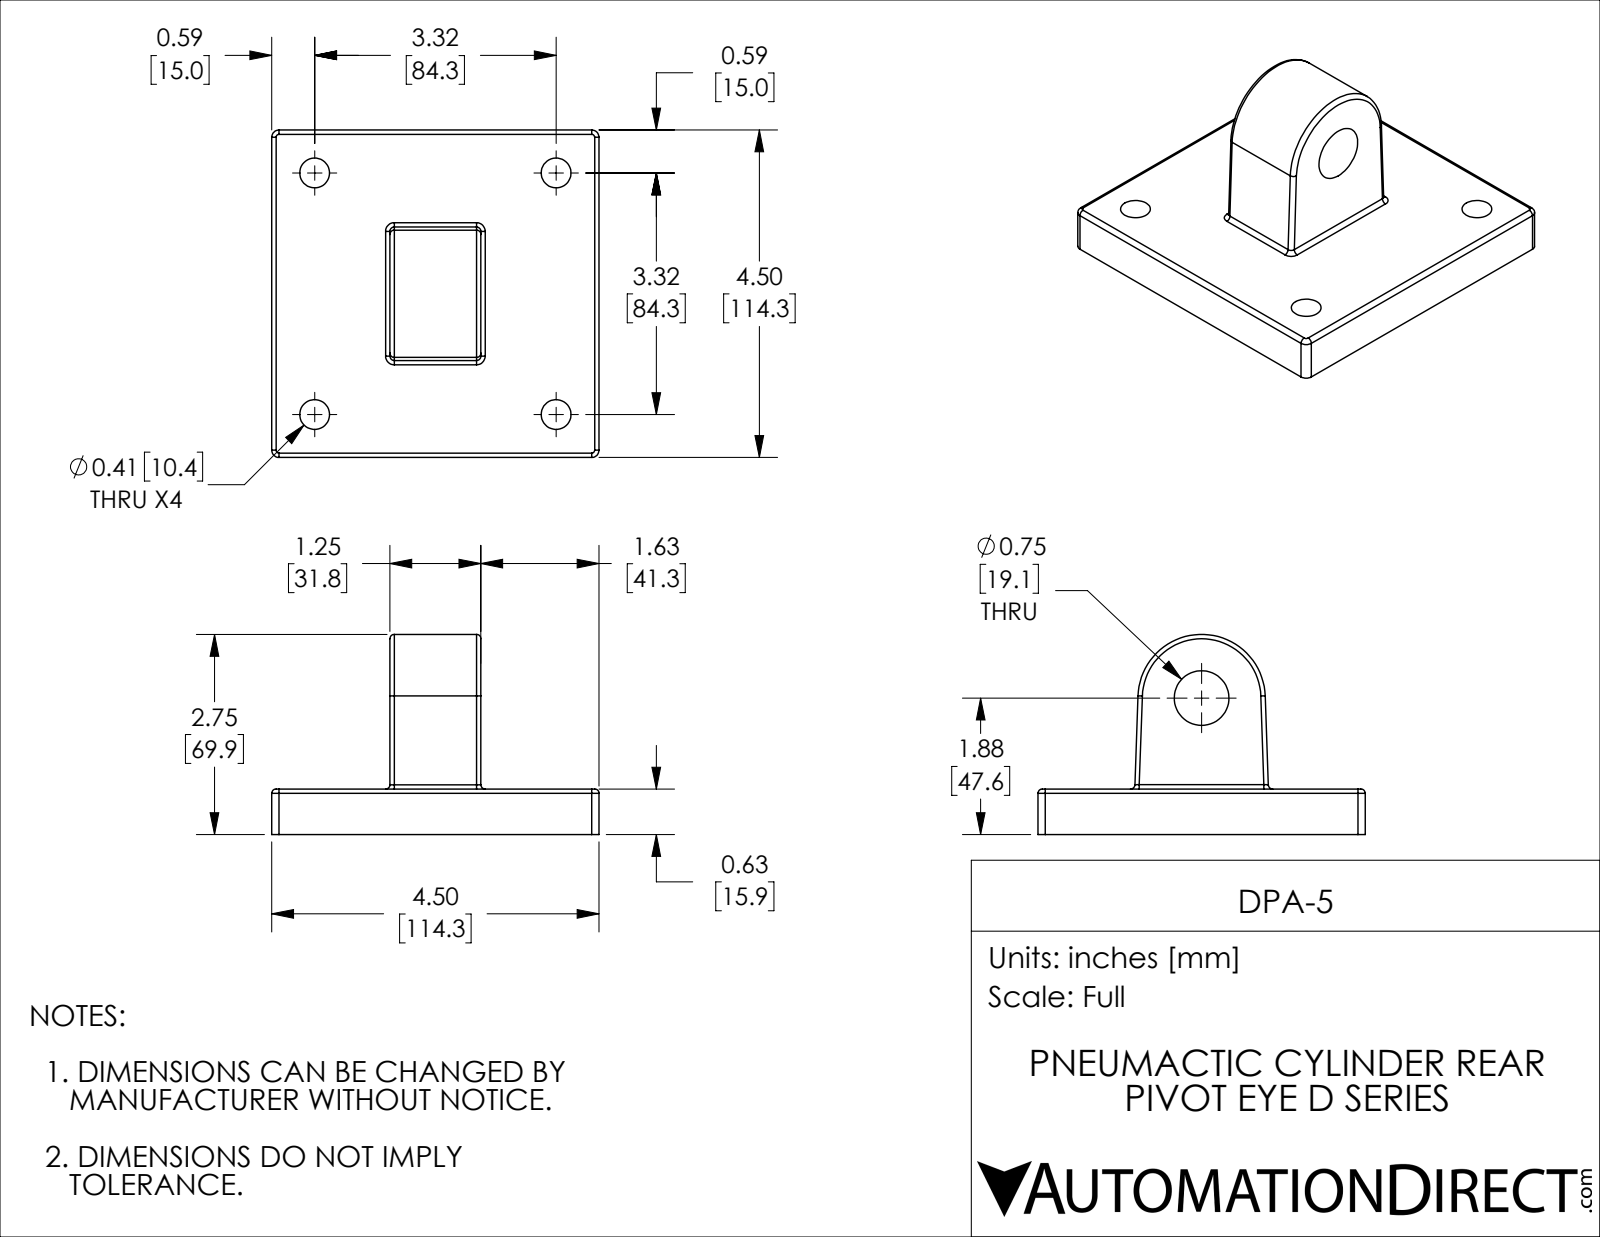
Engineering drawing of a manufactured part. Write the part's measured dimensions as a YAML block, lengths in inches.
part_name: "DPA-5"
step_written_by: "SolidWorks 2018 (AUTOMOTIVE_DESIGN)"
units: inches
bodies: {solids: 1, faces: 48, planar: 10, cylindrical: 28, other: 10}
overall_size: [4.5, 4.5, 2.75]
volume: 16.06
surface_area: 66.13
round_holes:
  - {diameter: 0.41, count: 4}
  - {diameter: 0.752, count: 1}
partial_cylinders:
  - {radius: 0.06, count: 12}
  - {radius: 0.1, count: 4}
  - {radius: 0.875, count: 1}
face_to_face_distances: [0.625, 1.625, 2.875, 4.5, 1.25]
hole_center_spacings: [3.32, 4.695]
